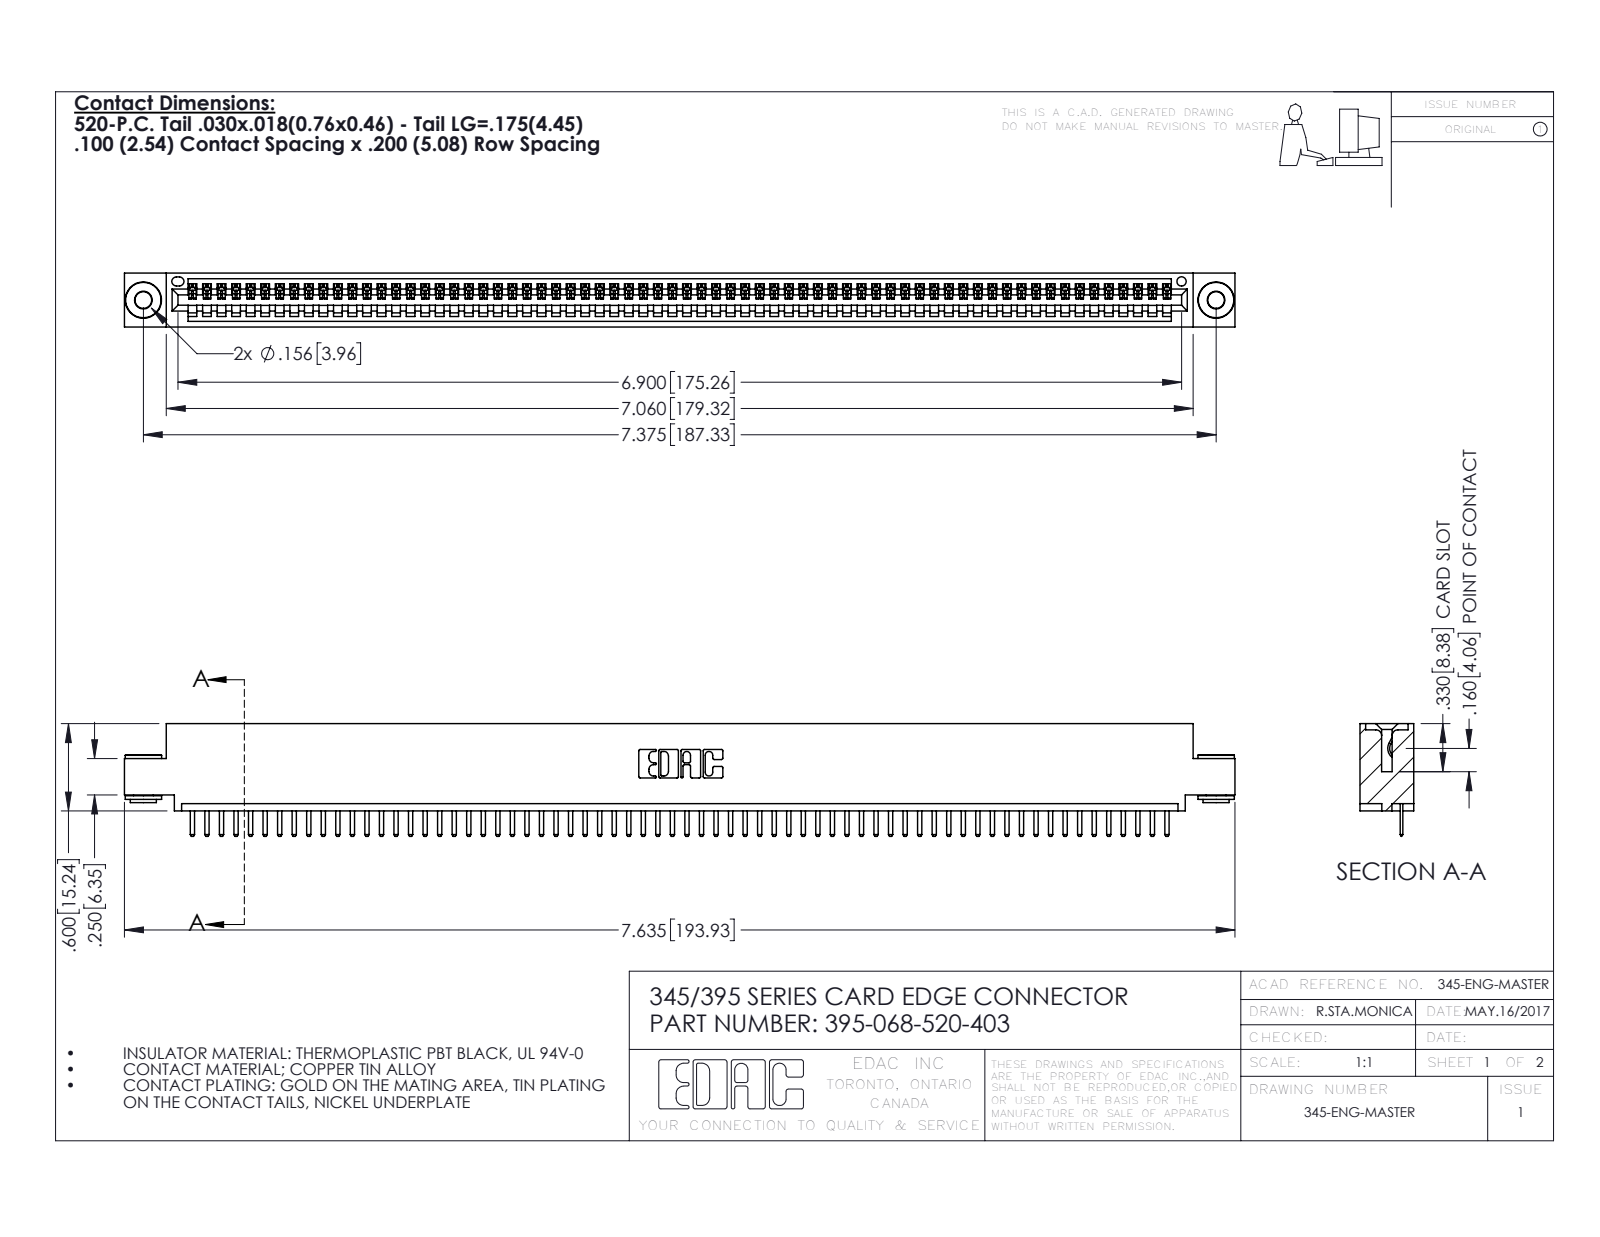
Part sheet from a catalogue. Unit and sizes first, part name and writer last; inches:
Units: inches
Overall size (bounding box): 7.635 × 0.775 × 0.37
Round holes (diameter × count): ⌀0.116 ×2, ⌀0.156 ×2, ⌀0.064 ×1
Round bosses / shafts (diameter × count): ⌀0.25 ×2, ⌀0.18 ×2, ⌀0.136 ×2
Partial cylindrical surfaces — rounded edges, fillets, slot ends (radius × count): R0.01 ×138, R0.006 ×136, R0.01 ×22, R0.007 ×6, R0.031 ×6, R0.026 ×3, R0.031 ×2, R0.04 ×2
Main face-to-face distances: 0.072, 0.298, 0.37, 0.2, 0.025, 0.098, 0.272, 0.225, 0.072, 0.149
Hole centre spacings: 0.27, 7.139, 7.375
Volume: 1.122 in³ · Surface area: 37.88 in²
Bodies: 71 solids, 4384 faces (2950 planar, 1426 cylindrical, 8 other)
Part name (STEP PRODUCT): 345-250-002_345-250-002-102; 345-292-001_345-293-120; 345 Part_0.110 Offset - 0.156 Dia-TH; 395-068-520-403
STEP written by: SolidWorks 2016 (CONFIG_CONTROL_DESIGN)
